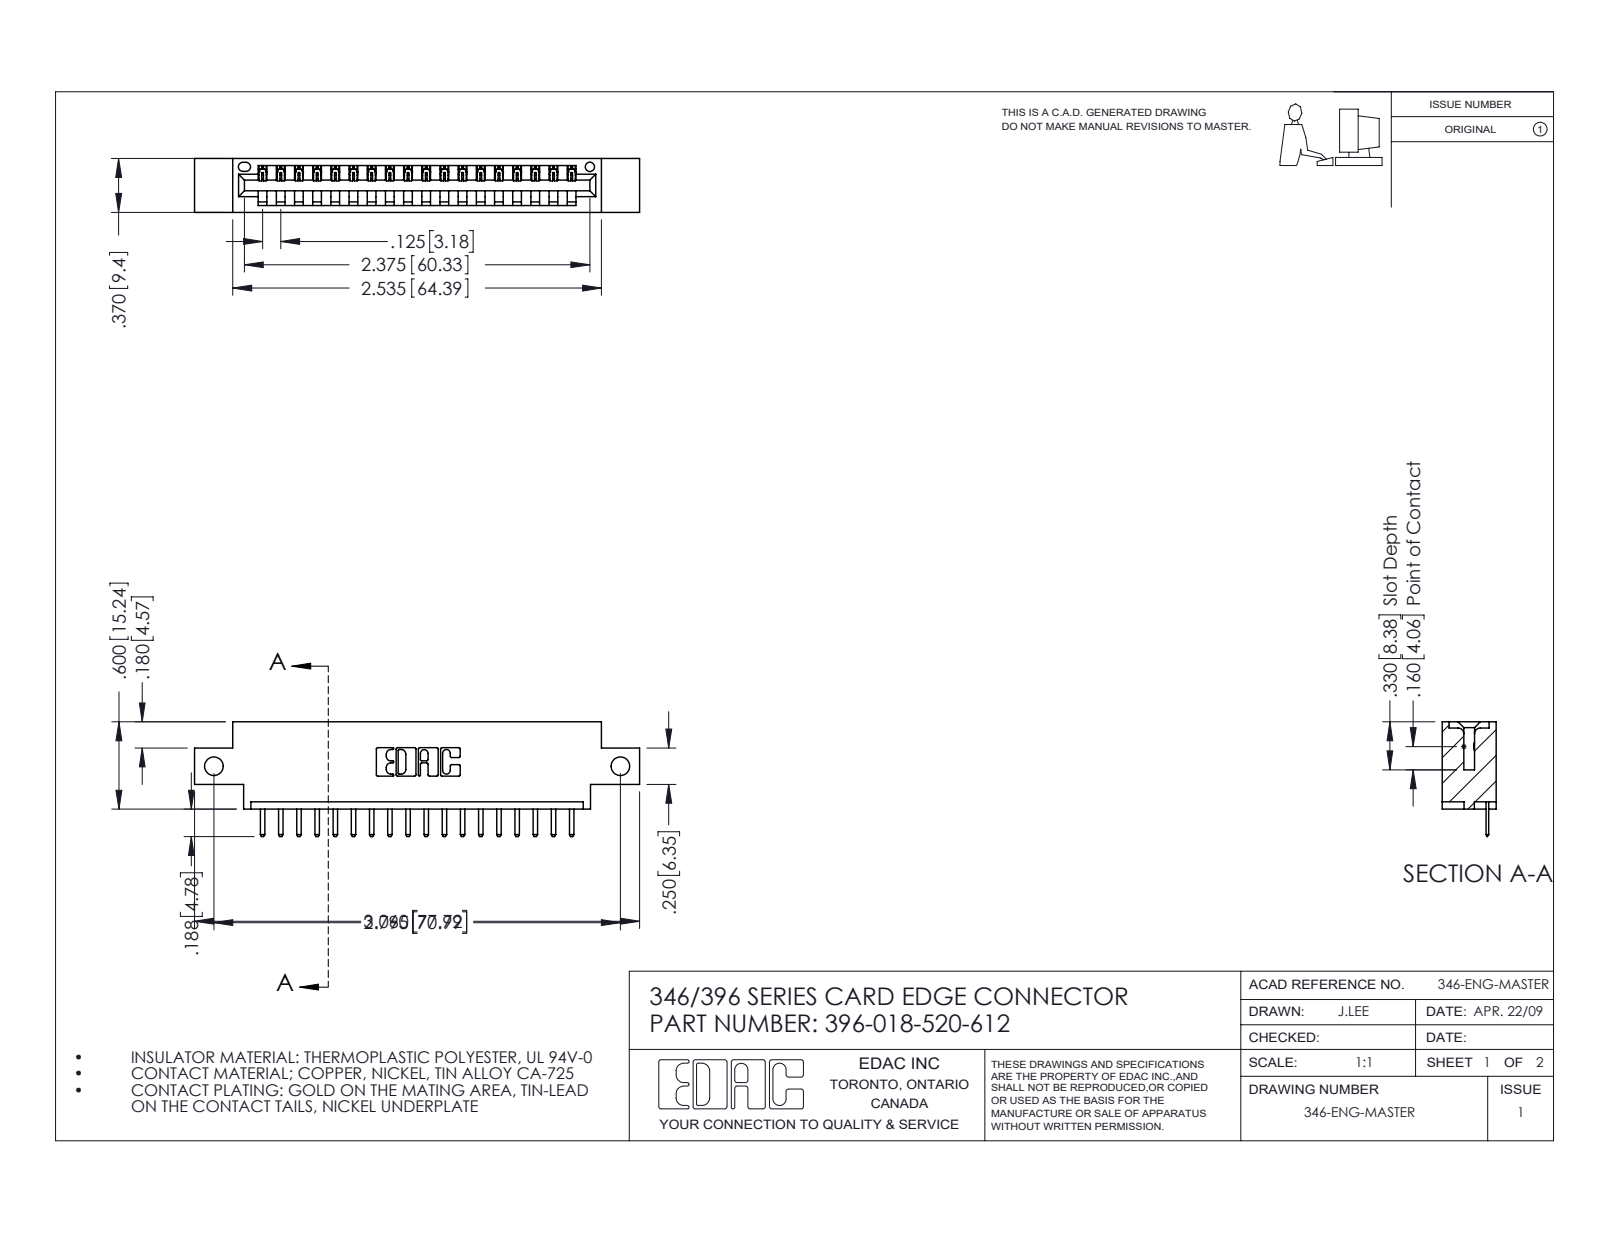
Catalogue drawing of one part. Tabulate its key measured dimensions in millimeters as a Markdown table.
| quantity | value |
| --- | --- |
| part name | 346 Part_0.170 Offset - Side Mount; 345-292-001_345-293-120; 396-018-520-612 |
| STEP written by | SolidWorks 2016 (CONFIG_CONTROL_DESIGN) |
| units | millimeters |
| bodies | 19 solids, 1242 faces (836 planar, 406 cylindrical, 0 other) |
| overall size | 77.7 × 20 × 9.4 |
| volume | 6 980 mm³ |
| surface area | 8 310 mm² |
| round holes (diameter × count) | 3.3 × 2, 1.6 × 1 |
| partial cylindrical surfaces (radius × count) | 0.3 × 38, 0.2 × 36, 0.3 × 22, 0.2 × 6, 0.8 × 6, 0.7 × 3, 0.8 × 2, 1 × 2 |
| main face-to-face distances | 9.4, 1.2, 8.2, 6.4, 3.8, 5.6, 2.5, 4.4, 1.8, 7.6 |
| hole center spacings | 71 |
